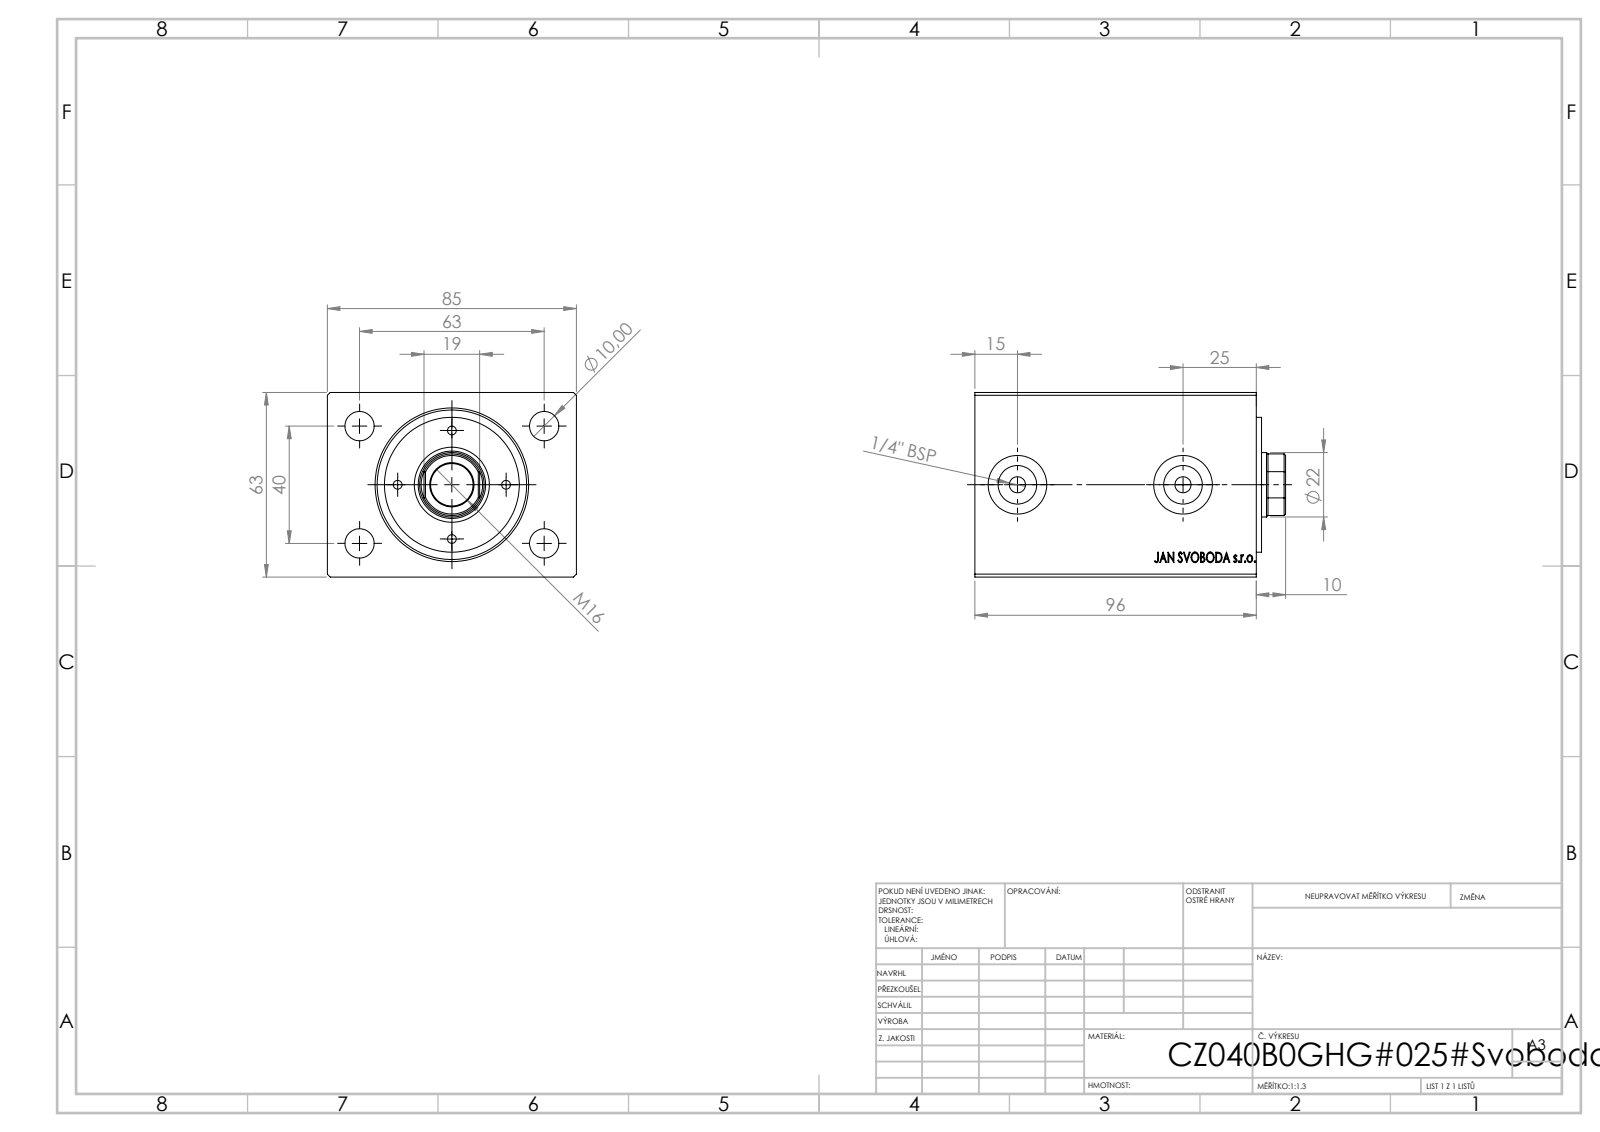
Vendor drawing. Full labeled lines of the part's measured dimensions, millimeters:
Part name (STEP PRODUCT): V500CZ; V500CZ_B_VC
STEP written by: SolidWorks 2019 (CONFIG_CONTROL_DESIGN)
Units: millimetres
Bodies: 3 solids, 874 faces (400 planar, 58 cylindrical, 416 other)
Overall size (bounding box): 106 × 85 × 63
Volume: 470 049 mm³ · Surface area: 75 067 mm²
Round holes (diameter × count): ⌀3 ×4, ⌀10 ×4, ⌀5.5 ×2, ⌀13.16 ×2, ⌀20 ×2, ⌀14.5 ×1, ⌀22 ×1, ⌀23 ×1, ⌀36 ×1, ⌀40 ×1, ⌀51 ×1
Round bosses / shafts (diameter × count): ⌀46 ×1
Partial cylindrical surfaces — rounded edges, fillets, slot ends (radius × count): R10.5 ×1
Main face-to-face distances: 63, 85, 96, 80.7, 15.3, 10, 1.8, 8.2, 72.5, 87.8
Hole centre spacings: 18.5, 23.85, 26.16, 31.54, 37.31, 49.74, 53.85, 37
